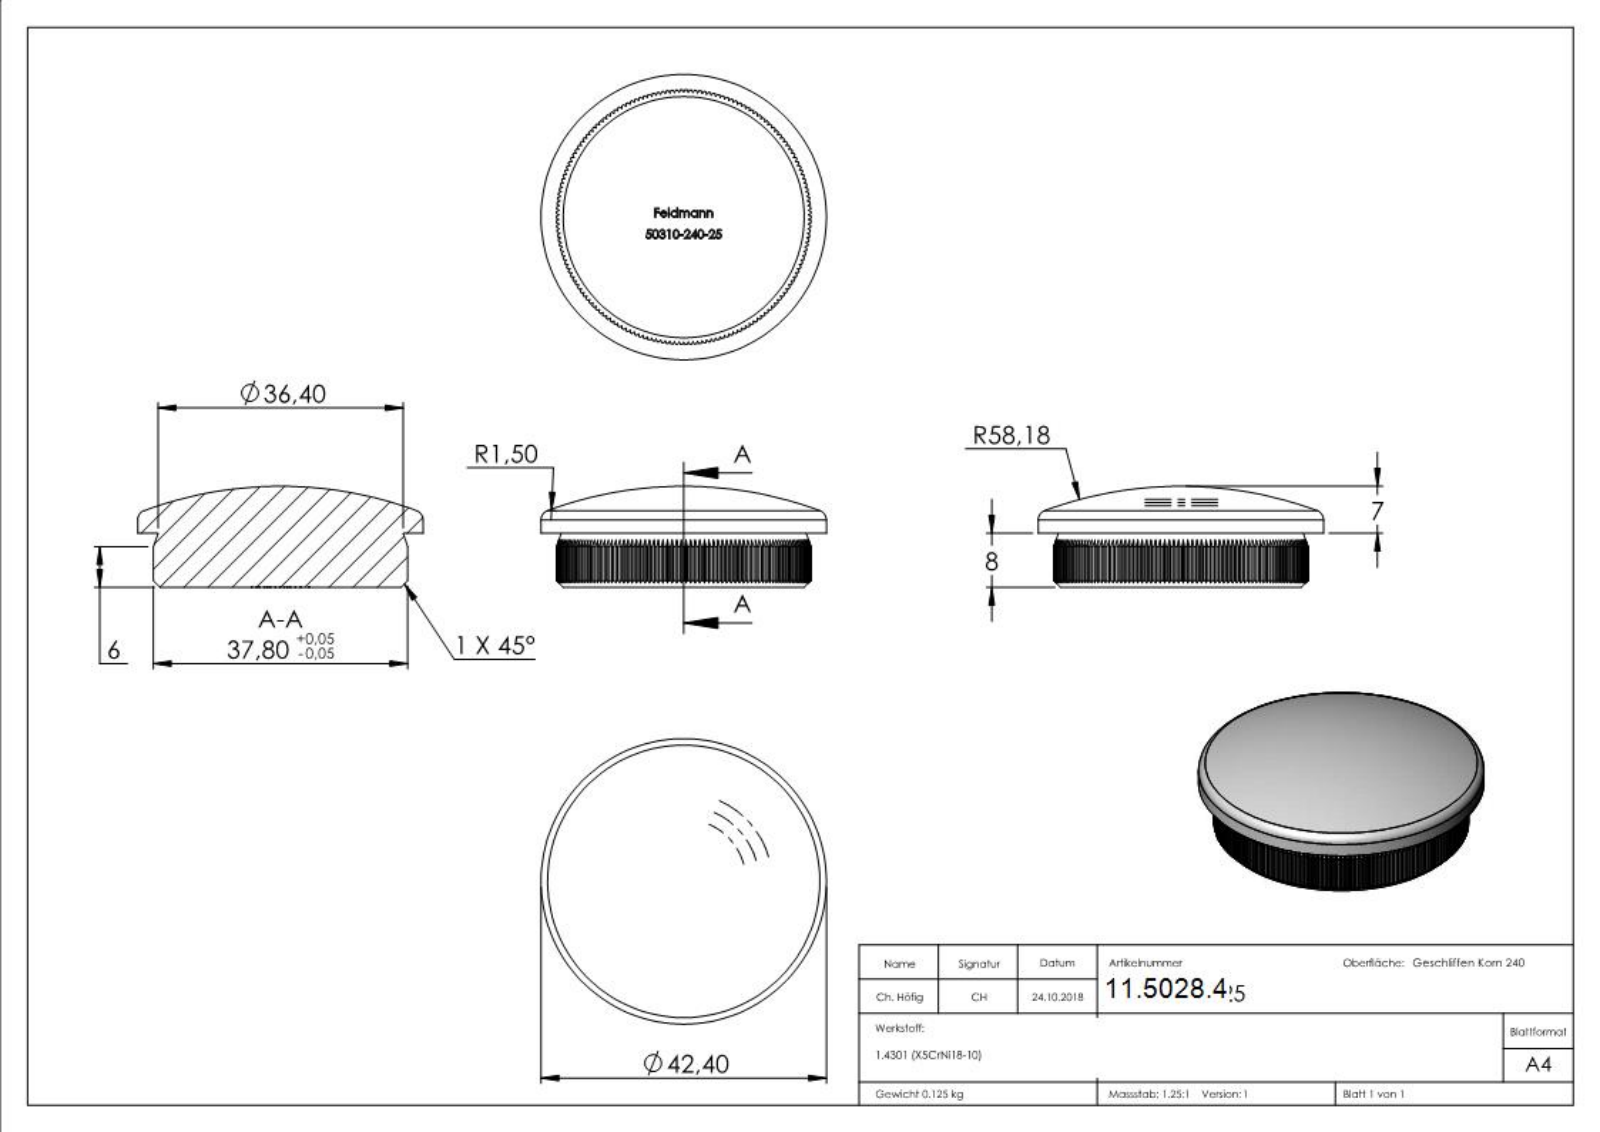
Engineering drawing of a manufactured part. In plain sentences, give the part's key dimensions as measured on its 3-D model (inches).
The part is named "50310-240-25". Its 3-D file was written by "SolidWorks 2015 (CONFIG_CONTROL_DESIGN)". It is 1 solid with 744 faces: 461 planar, 172 cylindrical and 111 other. Overall it measures 1.669 by 1.669 by 0.591 inches. Its volume is 0.967 cubic inches and its surface area 7.13 square inches. Round bosses or shafts: 1 of diameter 1.669. Partial cylindrical surfaces (rounded edges, fillets, slot ends): 1 of radius 0.744. The main face-to-face distances are 0.315, 0.731, 0.73, 0.731, 0.311, 0.729, 0.117, 0.015, 0.055, 0.133.
